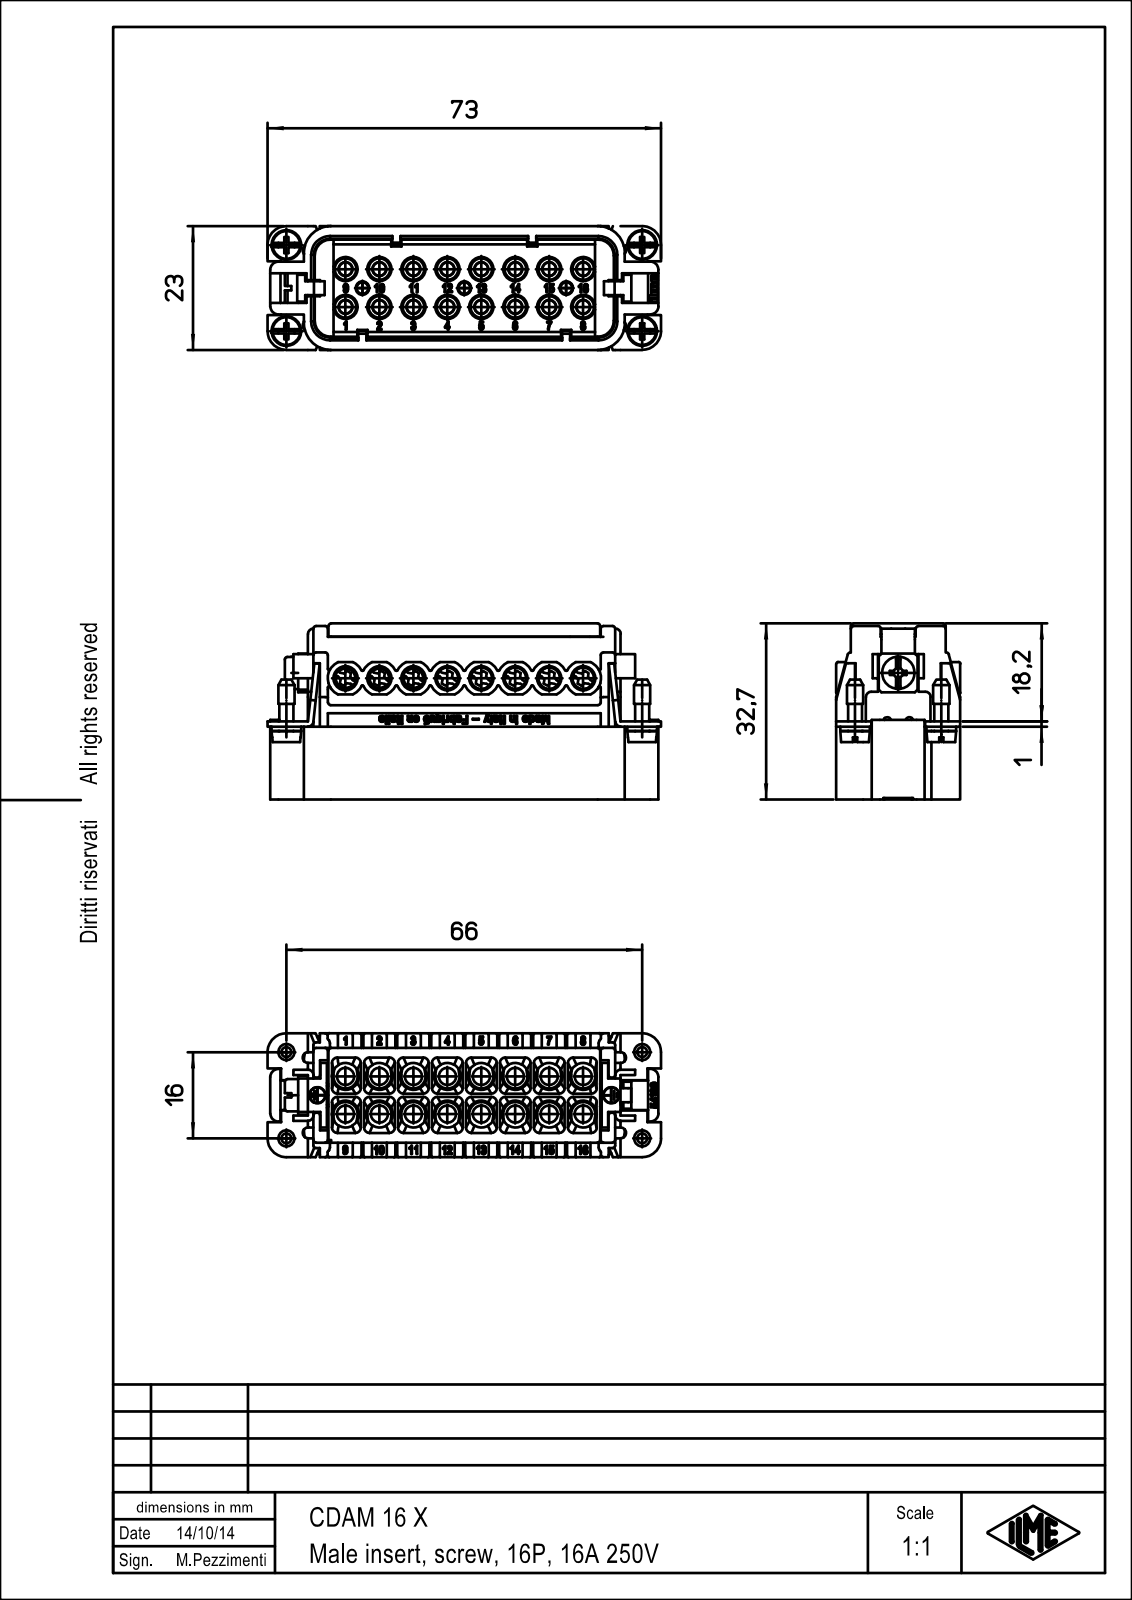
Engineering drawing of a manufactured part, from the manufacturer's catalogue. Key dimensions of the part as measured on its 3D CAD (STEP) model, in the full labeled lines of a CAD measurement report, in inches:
Part name (STEP PRODUCT): CDAM_16_X
STEP written by: PTC Creo Elements/Direct Modeling 19.0E 27-Jun-2016 (C) Parametric Technology GmbH (AUTOMOTIVE_DESIGN)
Units: inches
Bodies: 3 solids, 2026 faces (1440 planar, 319 cylindrical, 267 other)
Overall size (bounding box): 2.874 × 1.287 × 0.906
Round holes (diameter × count): ⌀0.197 ×16, ⌀0.157 ×8, ⌀0.118 ×4, ⌀0.071 ×1
Round bosses / shafts (diameter × count): ⌀0.098 ×16, ⌀0.217 ×4, ⌀0.102 ×4, ⌀0.236 ×1, ⌀0.177 ×1, ⌀0.138 ×1
Partial cylindrical surfaces — rounded edges, fillets, slot ends (radius × count): R0.039 ×20, R0.059 ×8, R0.13 ×8, R0.02 ×7, R0.079 ×4, R0.118 ×4, R0.138 ×4, R0.197 ×4
Main face-to-face distances: 0.039, 0.906, 0.079, 0.677, 0.106, 0.799, 0.598, 0.531, 0.157, 0.52
Hole centre spacings: 0.248, 0.496, 0.744, 0.371, 0.567, 0.992, 0.793, 1.24
